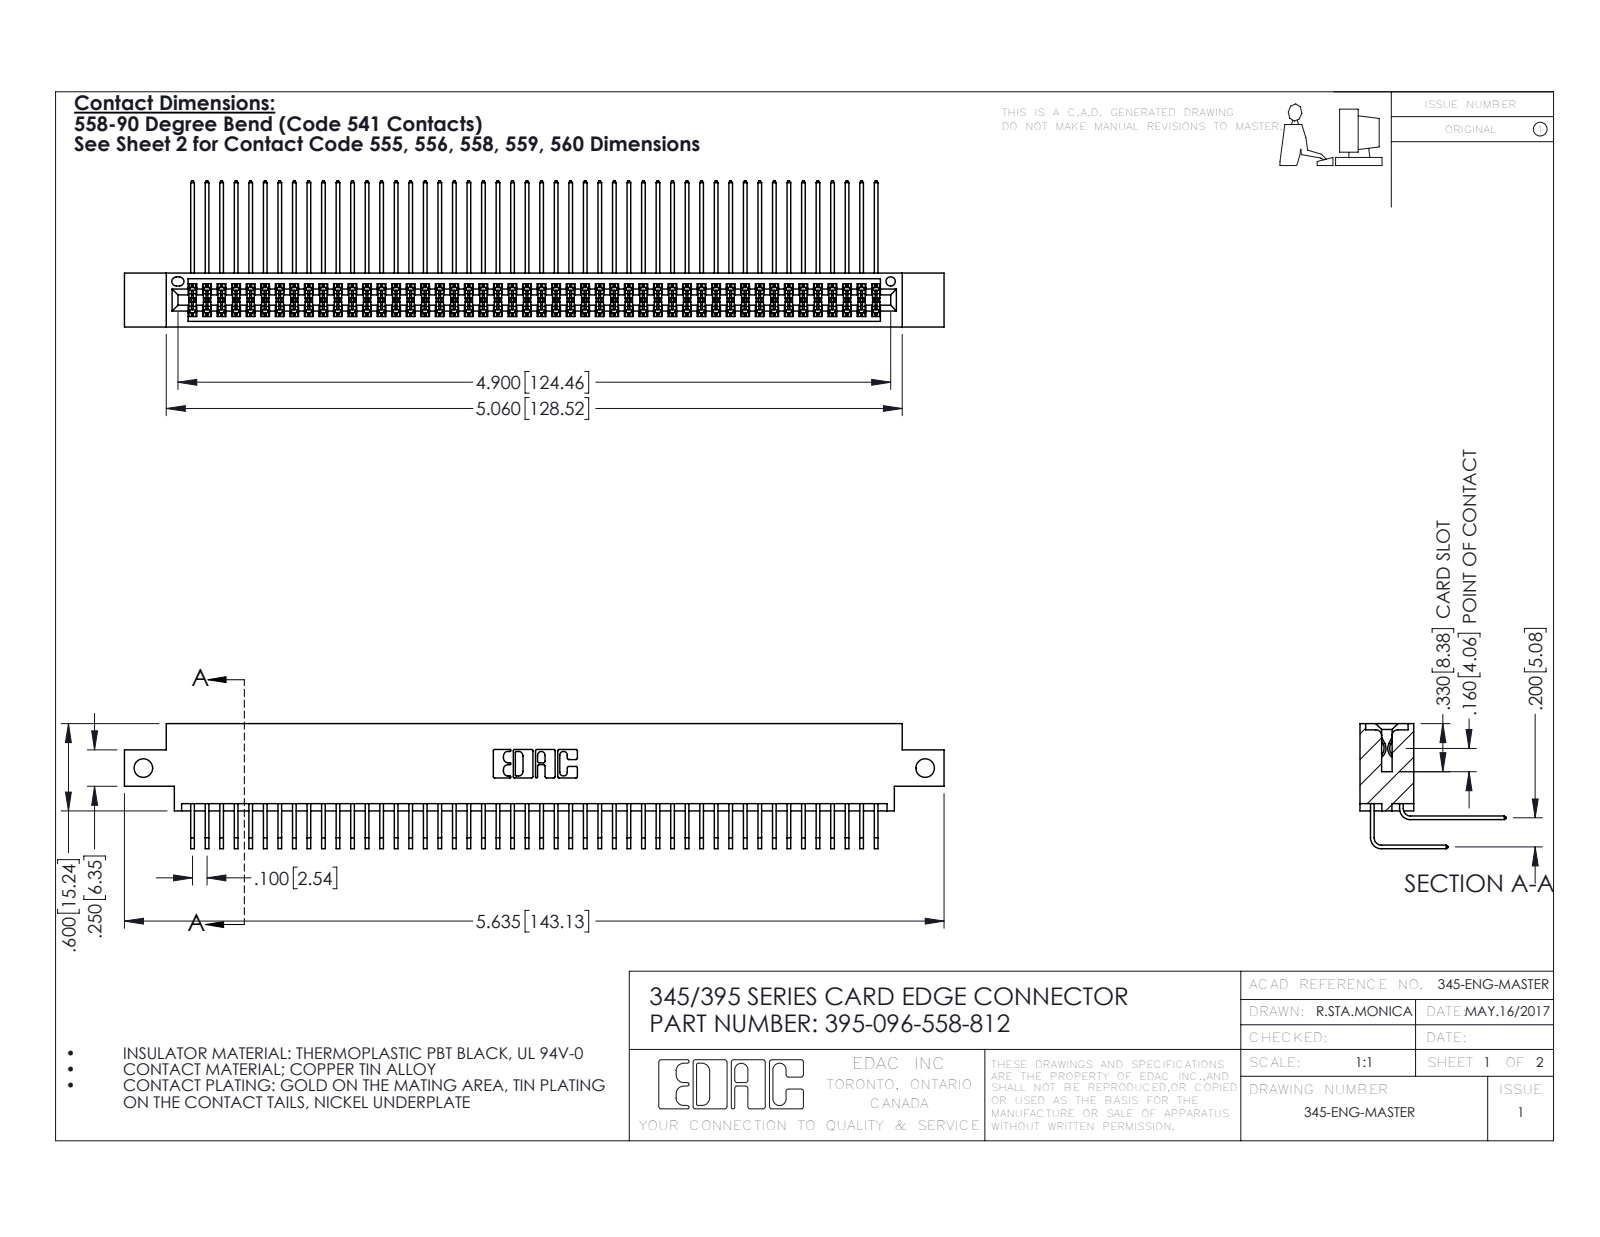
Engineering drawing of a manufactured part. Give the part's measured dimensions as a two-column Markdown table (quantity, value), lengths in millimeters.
| quantity | value |
| --- | --- |
| part name | 395-096-558-812; 345 Part_0.170 Offset - Side Mount; 345-292-001_558 559 Tail - 1; 345-292-001_558 Tail - 2 |
| STEP written by | SolidWorks 2016 (CONFIG_CONTROL_DESIGN) |
| units | millimeters |
| bodies | 97 solids, 5122 faces (3444 planar, 1678 cylindrical, 0 other) |
| overall size | 143.1 × 25.5 × 21.8 |
| volume | 14 300 mm³ |
| surface area | 23 880 mm² |
| round holes (diameter × count) | 3.3 × 2, 1.6 × 1 |
| partial cylindrical surfaces (radius × count) | 0.2 × 145, 0.3 × 22, 0.2 × 6, 0.8 × 6, 0.7 × 3, 0.4 × 2, 0.5 × 2, 0.6 × 2 |
| main face-to-face distances | 1.8, 7.6, 5.1, 9.4, 2.5, 6.9, 0.6, 5.7, 4.4, 0.6 |
| hole center spacings | 136.5 |
